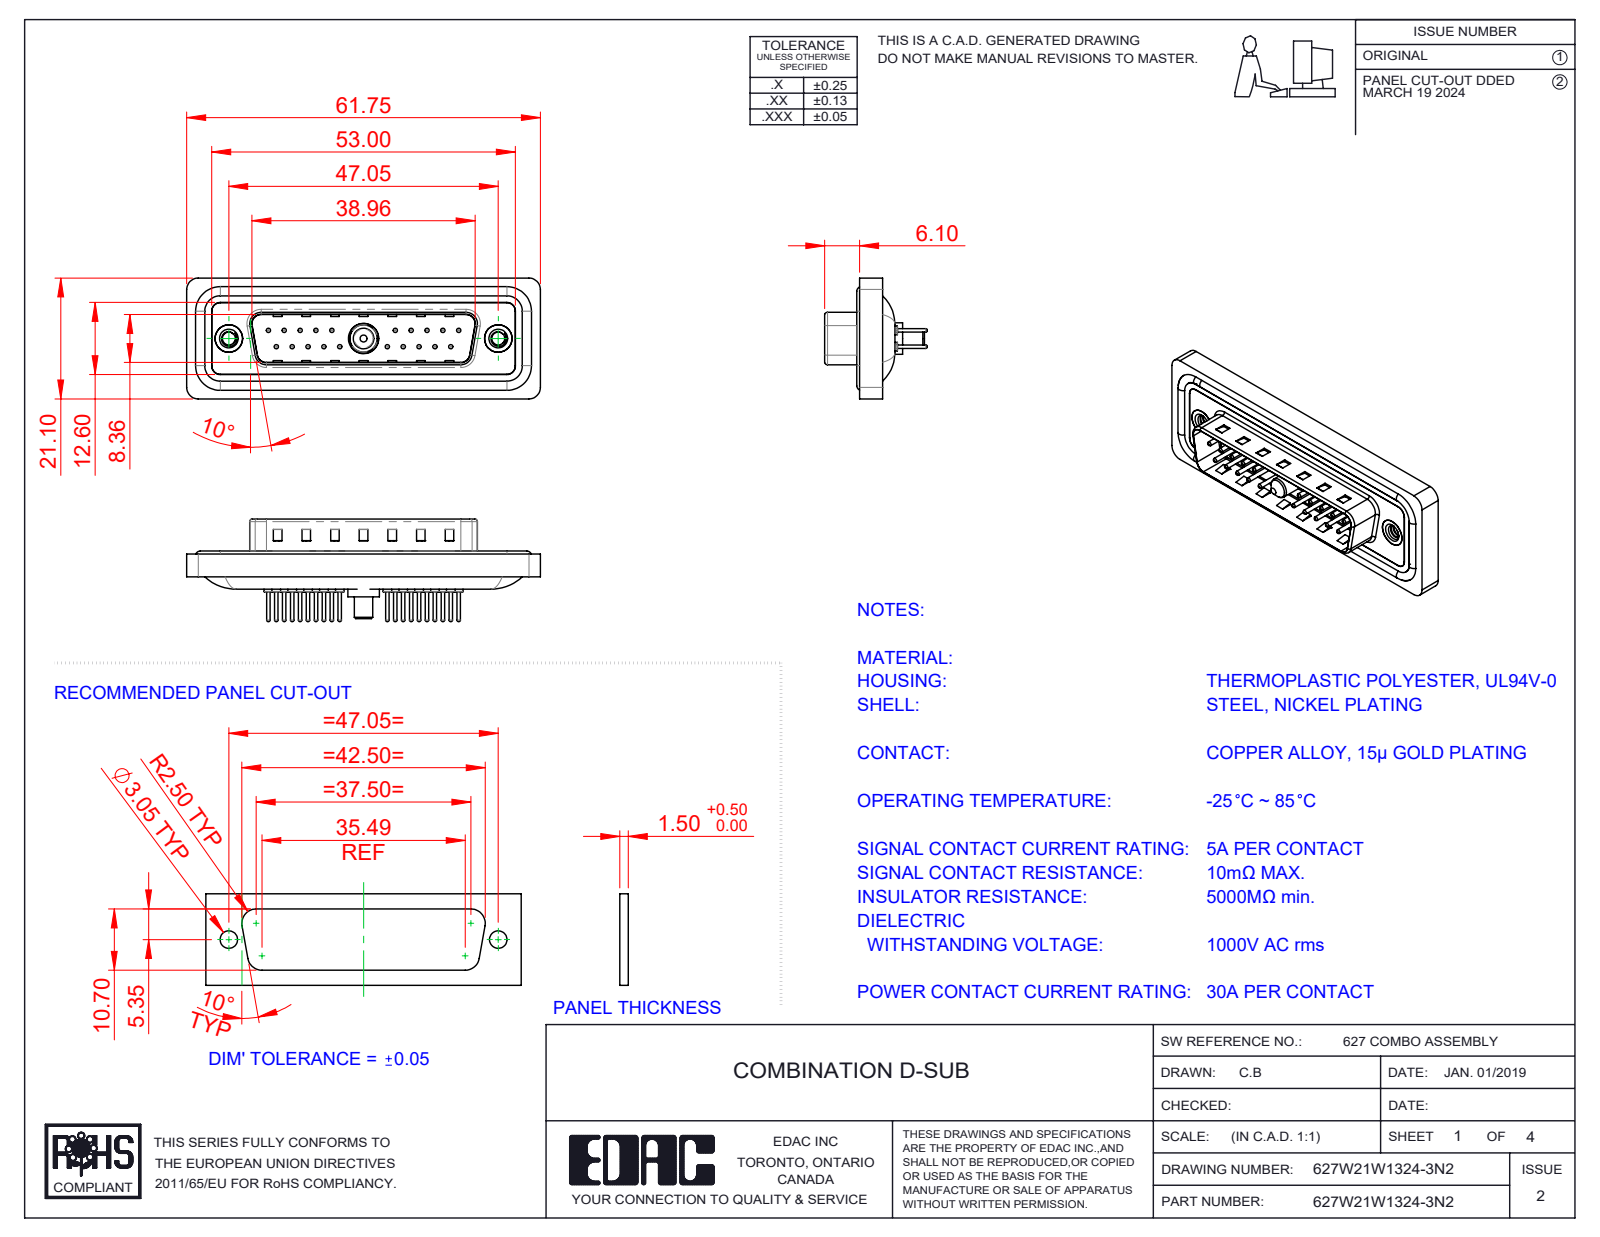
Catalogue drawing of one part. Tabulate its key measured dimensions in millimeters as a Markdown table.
| quantity | value |
| --- | --- |
| part name | 627Combo Shell Front_25 Contacts; 627Combo Threaded Rivet_2; 627Combo Housing_21W1; 627Combo Waterproof Housing_25 Contacts (+5 more) |
| STEP written by | SolidWorks 2023 (CONFIG_CONTROL_DESIGN) |
| units | millimeters |
| bodies | 29 solids, 1262 faces (359 planar, 487 cylindrical, 416 other) |
| overall size | 61.75 × 21.1 × 17.9 |
| volume | 7 205 mm³ |
| surface area | 11 958 mm² |
| round holes (diameter × count) | 0.75 × 20, 1.6 × 20, 2 × 20, 2.26 × 2, 4 × 2, 4.8 × 2, 5 × 2, 4.85 × 1, 5.3 × 1 |
| round bosses / shafts (diameter × count) | 1.5 × 20, 0.6 × 20, 1.6 × 4, 4.9 × 2, 5.5 × 1, 5.2 × 1, 4.75 × 1, 3.75 × 1 |
| partial cylindrical surfaces (radius × count) | 1.5 × 22, 2 × 18, 0.5 × 8, 1.6 × 8, 0.25 × 4, 0.6 × 4, 0.65 × 4, 0.9 × 4 |
| main face-to-face distances | 0.4, 1.5, 1.1, 1.6, 0.5, 3.1, 2.9, 4.1, 0.82, 9.58 |
| hole center spacings | 3.16, 2.77, 5.54, 8.31, 5.04, 19.39, 20.97, 22.16 |
